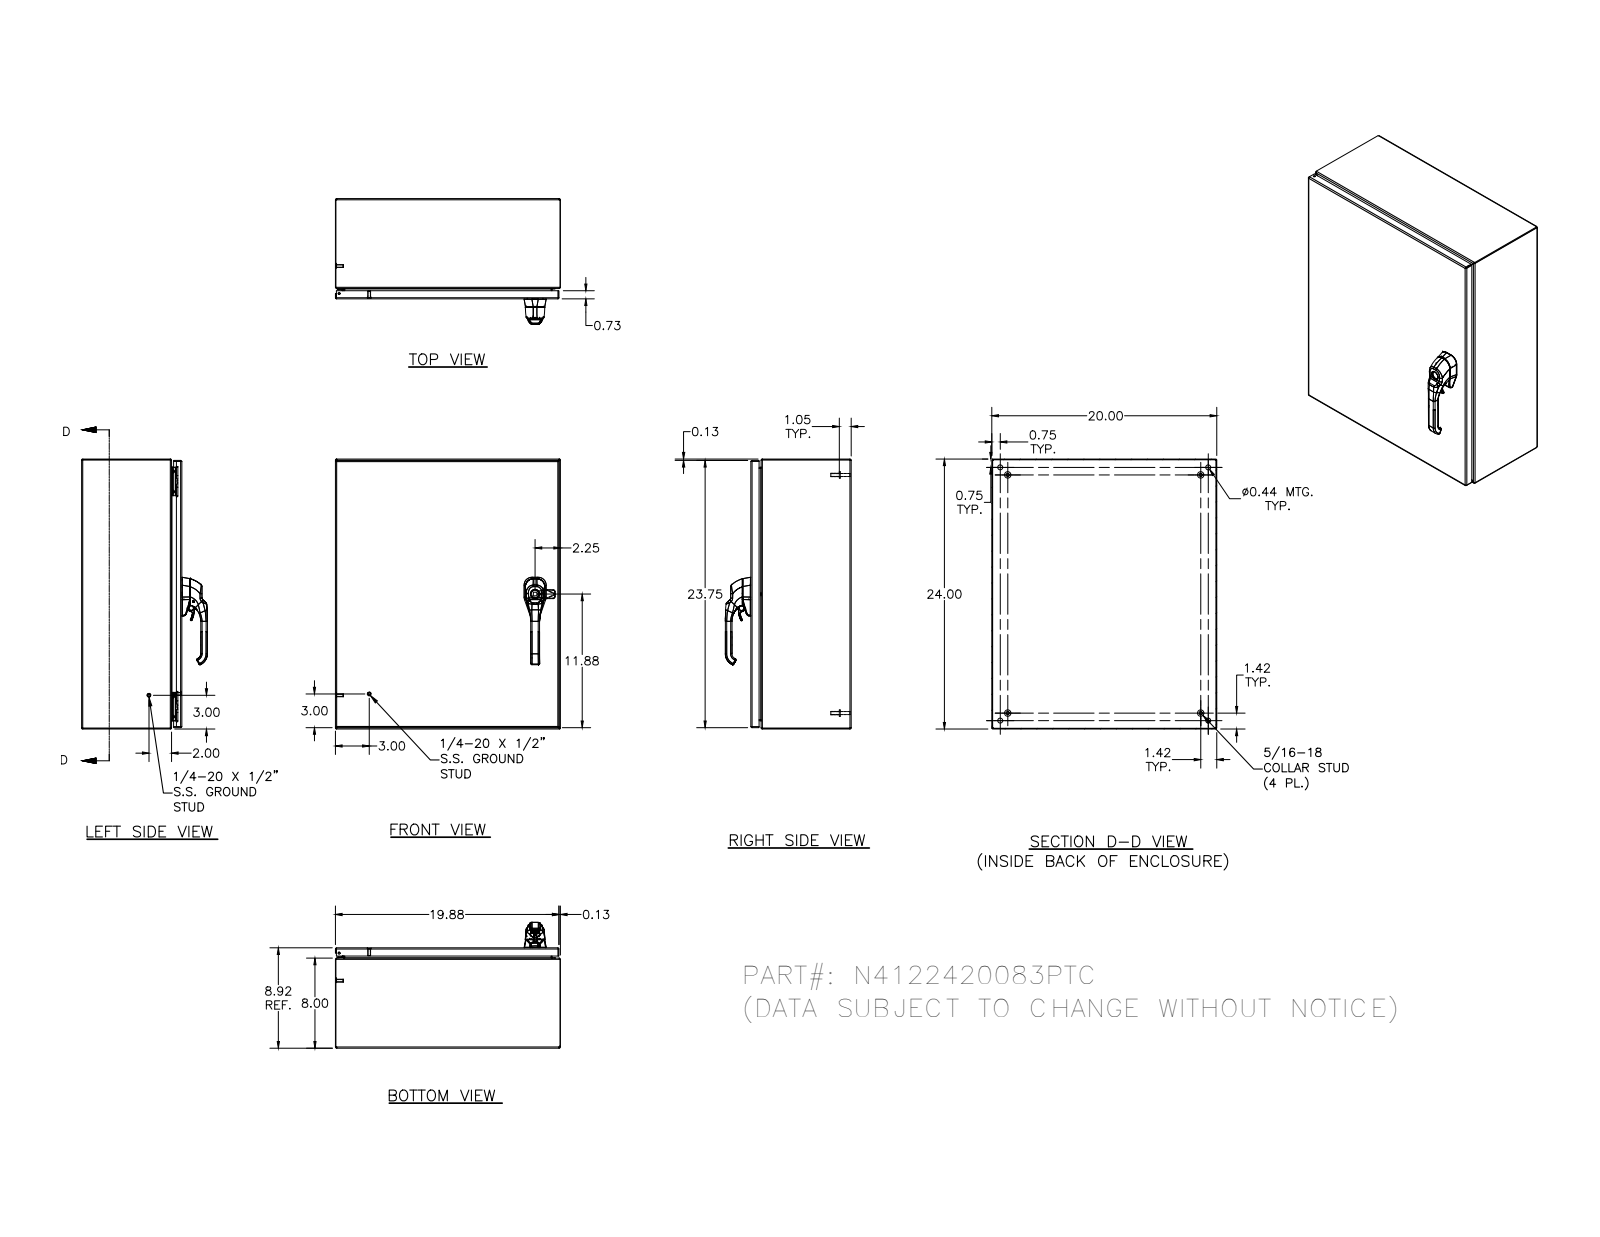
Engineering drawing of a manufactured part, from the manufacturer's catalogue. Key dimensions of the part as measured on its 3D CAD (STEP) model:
Part name (STEP PRODUCT): N4122420083PTC
STEP written by: SolidWorks 2018 (AUTOMOTIVE_DESIGN)
Units: inches
Bodies: 29 solids, 1333 faces (433 planar, 495 cylindrical, 405 other)
Overall size (bounding box): 24 × 20 × 11.095
Volume: 145.8 in³ · Surface area: 3 737 in²
Round holes (diameter × count): ⌀0.188 ×5, ⌀0.093 ×4, ⌀0.152 ×4, ⌀0.167 ×4, ⌀0.172 ×4, ⌀0.437 ×4, ⌀0.156 ×2, ⌀0.187 ×1, ⌀0.413 ×1
Round bosses / shafts (diameter × count): ⌀0.25 ×10, ⌀0.563 ×4, ⌀0.36 ×4, ⌀0.32 ×4, ⌀0.3 ×4, ⌀0.275 ×4, ⌀0.256 ×4, ⌀0.164 ×4
Partial cylindrical surfaces — rounded edges, fillets, slot ends (radius × count): R0.031 ×30, R0.05 ×26, R0.105 ×20, R0.016 ×18, R0.125 ×14, R0.02 ×11, R0.032 ×8, R0.067 ×8
Main face-to-face distances: 0.074, 8.843, 8.917, 8.769, 19.926, 23.926, 20, 19.852, 24, 23.852
Hole centre spacings: 19.996, 18.872, 0.017, 0.66, 20.656, 0.019, 0.5, 0.648
